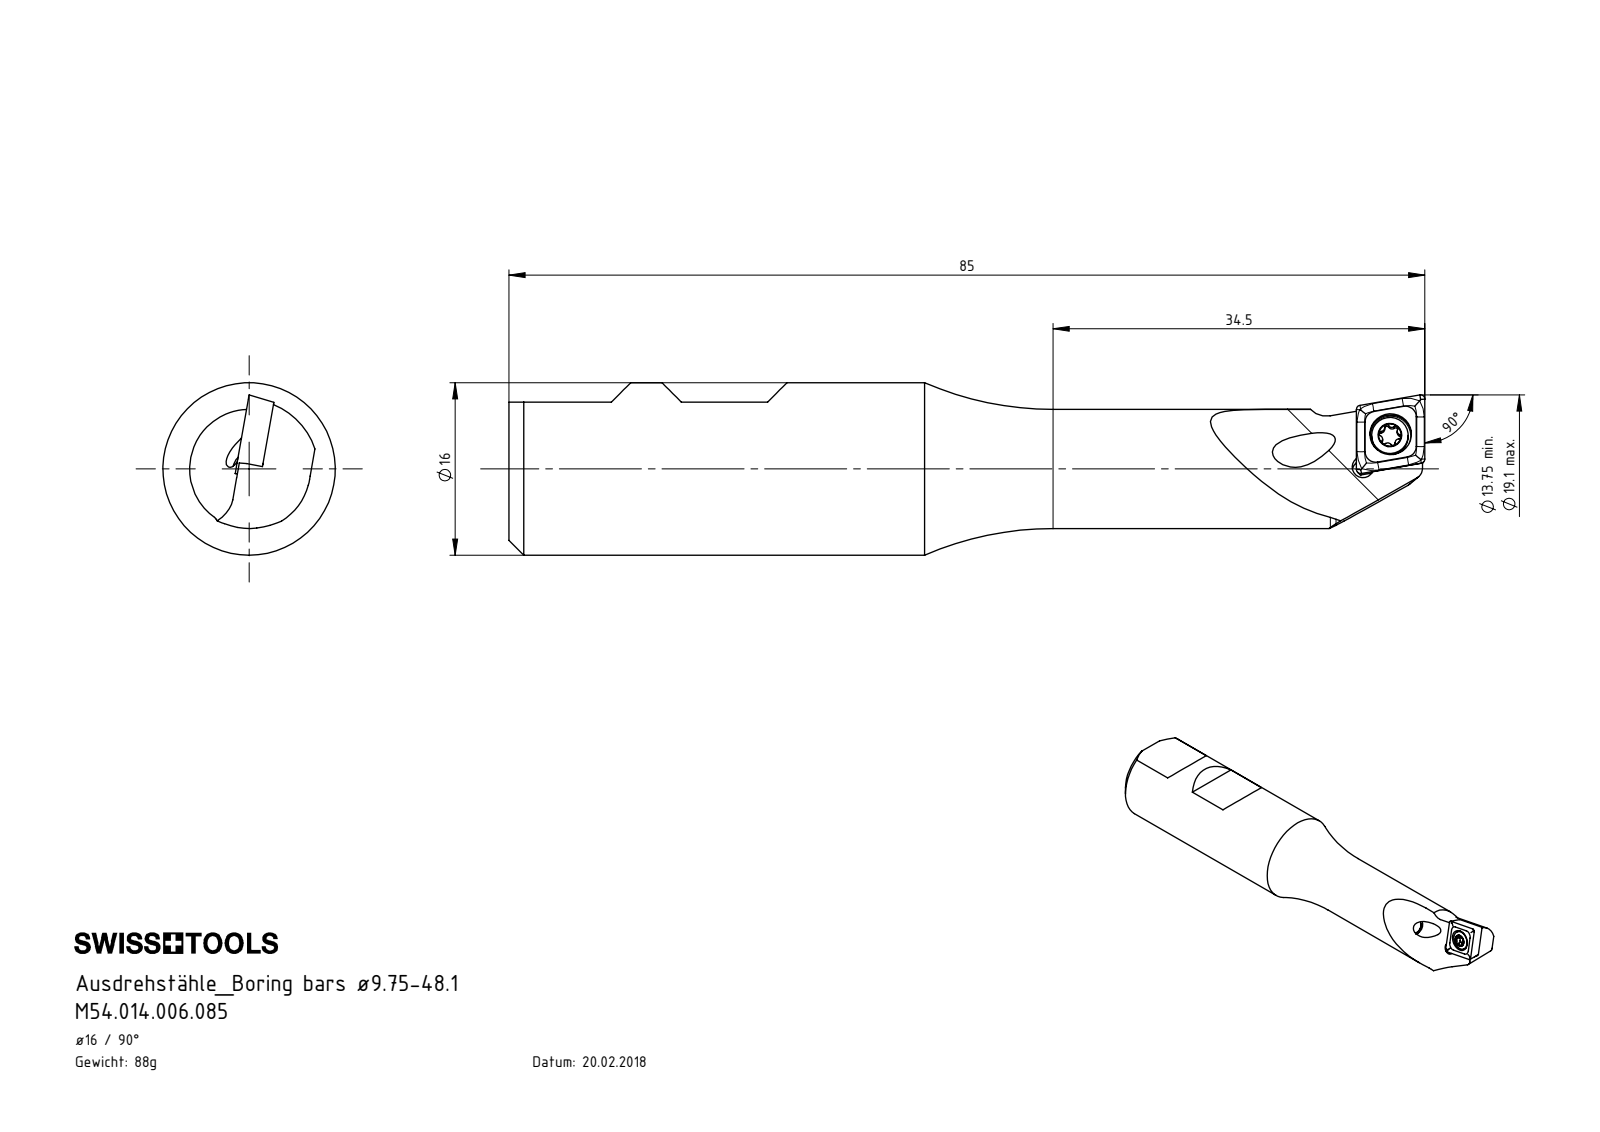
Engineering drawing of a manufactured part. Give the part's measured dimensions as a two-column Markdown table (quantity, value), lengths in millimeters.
| quantity | value |
| --- | --- |
| part name | B14.WCA.K11.085; CCMT060204; WCA-ER2.001.006_A; B14-WCA.K11.085_A |
| STEP written by | SolidWorks 2017 (AUTOMOTIVE_DESIGN) |
| units | millimeters |
| bodies | 3 solids, 102 faces (33 planar, 27 cylindrical, 42 other) |
| overall size | 85 × 16 × 16 |
| volume | 11 149 mm³ |
| surface area | 4 644 mm² |
| round holes (diameter × count) | 3 × 2, 2 × 1, 2.05 × 1, 2.8 × 1, 3.85 × 1 |
| round bosses / shafts (diameter × count) | 16 × 1, 11.05 × 1, 3.4 × 1, 2.5 × 1 |
| partial cylindrical surfaces (radius × count) | 0.21 × 6, 0.36 × 5, 0.36 × 1, 1 × 1, 5.7 × 1, 6.5 × 1, 8 × 1 |
| main face-to-face distances | 2.17, 2.18, 10.25, 4.51, 4.52, 6.69, 6.9, 2.39, 2.38, 78.76 |
| hole center spacings | 3.89, 3.99 |
